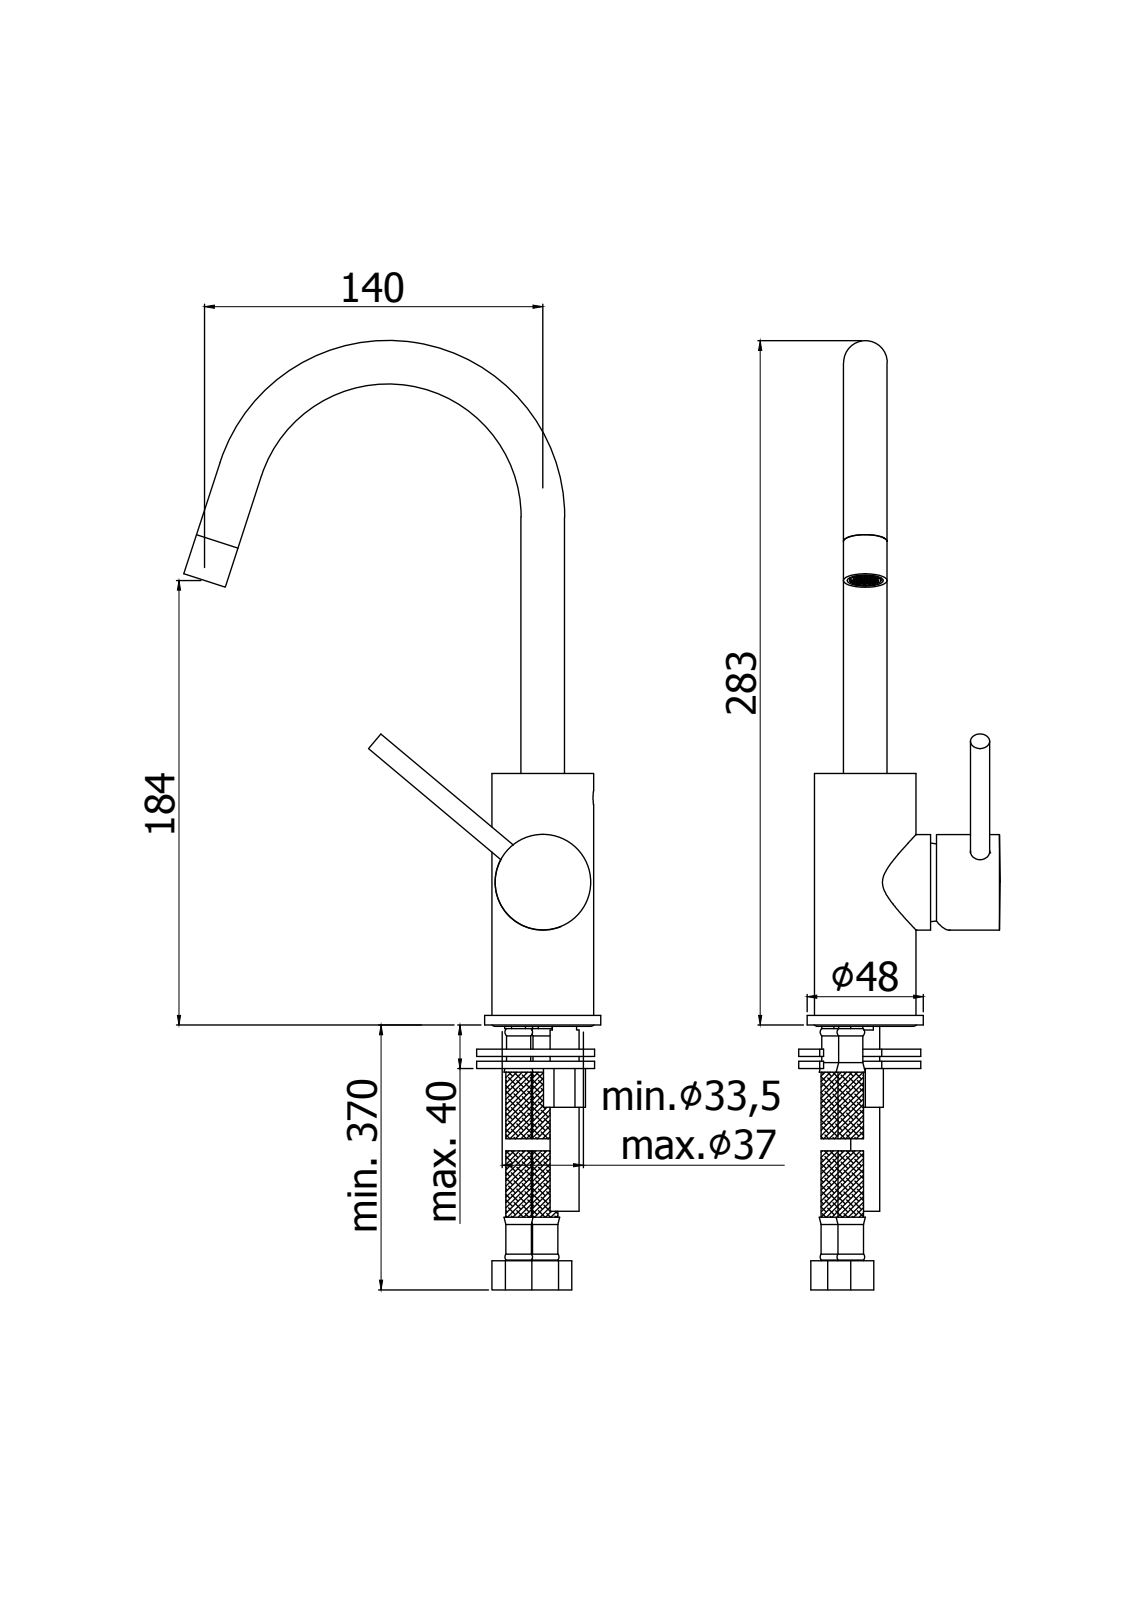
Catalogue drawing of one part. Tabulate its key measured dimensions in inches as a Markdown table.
| quantity | value |
| --- | --- |
| part name | LIG078CR |
| STEP written by | CREO PARAMETRIC BY PTC INC, 2020044 (CONFIG_CONTROL_DESIGN) |
| units | inches |
| bodies | 2 solids, 1184 faces (290 planar, 569 cylindrical, 325 other) |
| overall size | 11.126 × 6.764 × 3.116 |
| volume | 10.28 in³ |
| surface area | 137.4 in² |
| round holes (diameter × count) | 0.02 × 51, 0.118 × 2, 0.197 × 2, 0.236 × 2, 0.256 × 2, 0.276 × 2, 0.339 × 2, 0.362 × 2, 0.63 × 2, 1.043 × 2, 0.157 × 1, 0.177 × 1 |
| round bosses / shafts (diameter × count) | 0.626 × 2, 1.89 × 1, 1.654 × 1, 1.555 × 1, 1.516 × 1, 1.122 × 1, 1.094 × 1, 0.984 × 1 |
| partial cylindrical surfaces (radius × count) | 0.02 × 62, 0.039 × 20, 0.028 × 10, 0.031 × 6, 0.024 × 4, 0.026 × 4, 0.033 × 4, 0.079 × 4 |
| main face-to-face distances | 0.079, 0.118, 0.276, 3.819, 0.138, 0.094, 0.157, 0.236, 0.016, 3.843 |
| hole center spacings | 0.059, 0.118, 0.132, 0.083, 0.132, 0.213, 0.187, 0.177 |
